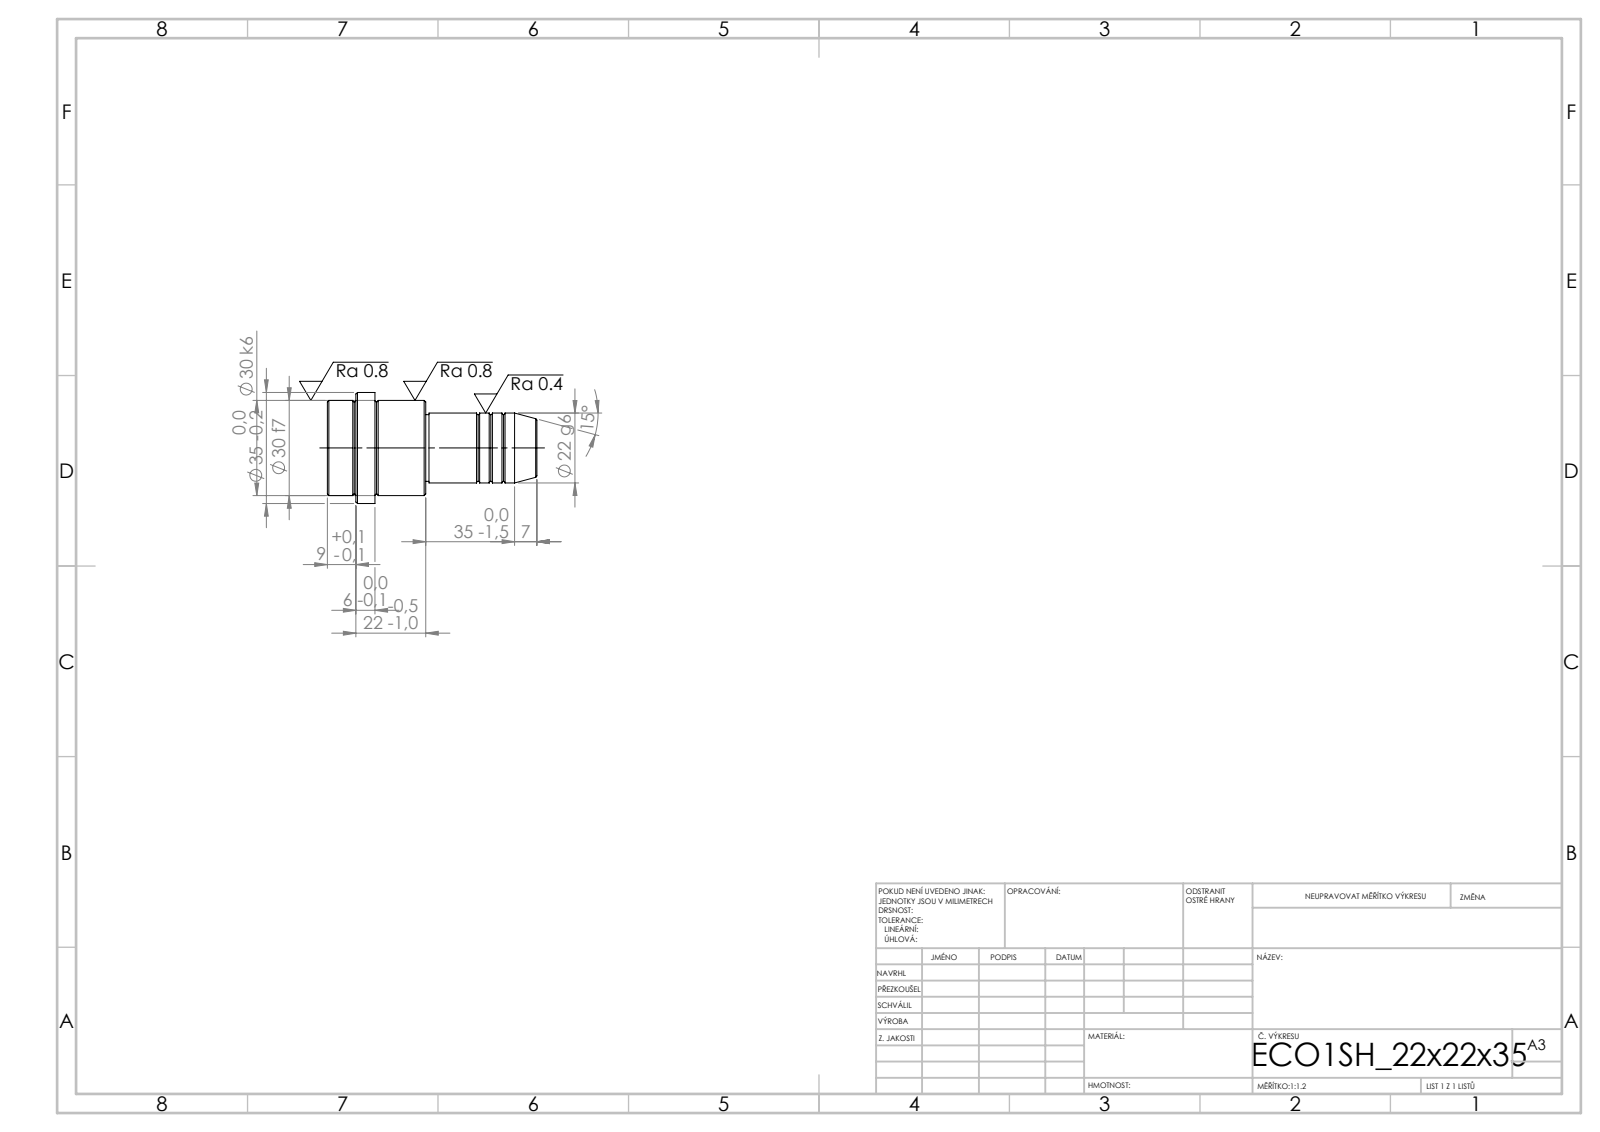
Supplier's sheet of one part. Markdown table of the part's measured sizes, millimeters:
| quantity | value |
| --- | --- |
| STEP written by | SolidWorks 2019 (CONFIG_CONTROL_DESIGN) |
| units | millimeters |
| bodies | 1 solid, 52 faces (6 planar, 16 cylindrical, 30 other) |
| overall size | 66 × 35 × 35 |
| volume | 36 096 mm³ |
| surface area | 7 395 mm² |
| round bosses / shafts (diameter × count) | 35 × 1, 30 × 1, 22 × 1, 21 × 1 |
| main face-to-face distances | 31, 16, 15, 35, 51, 66, 57, 22, 6, 9 |
